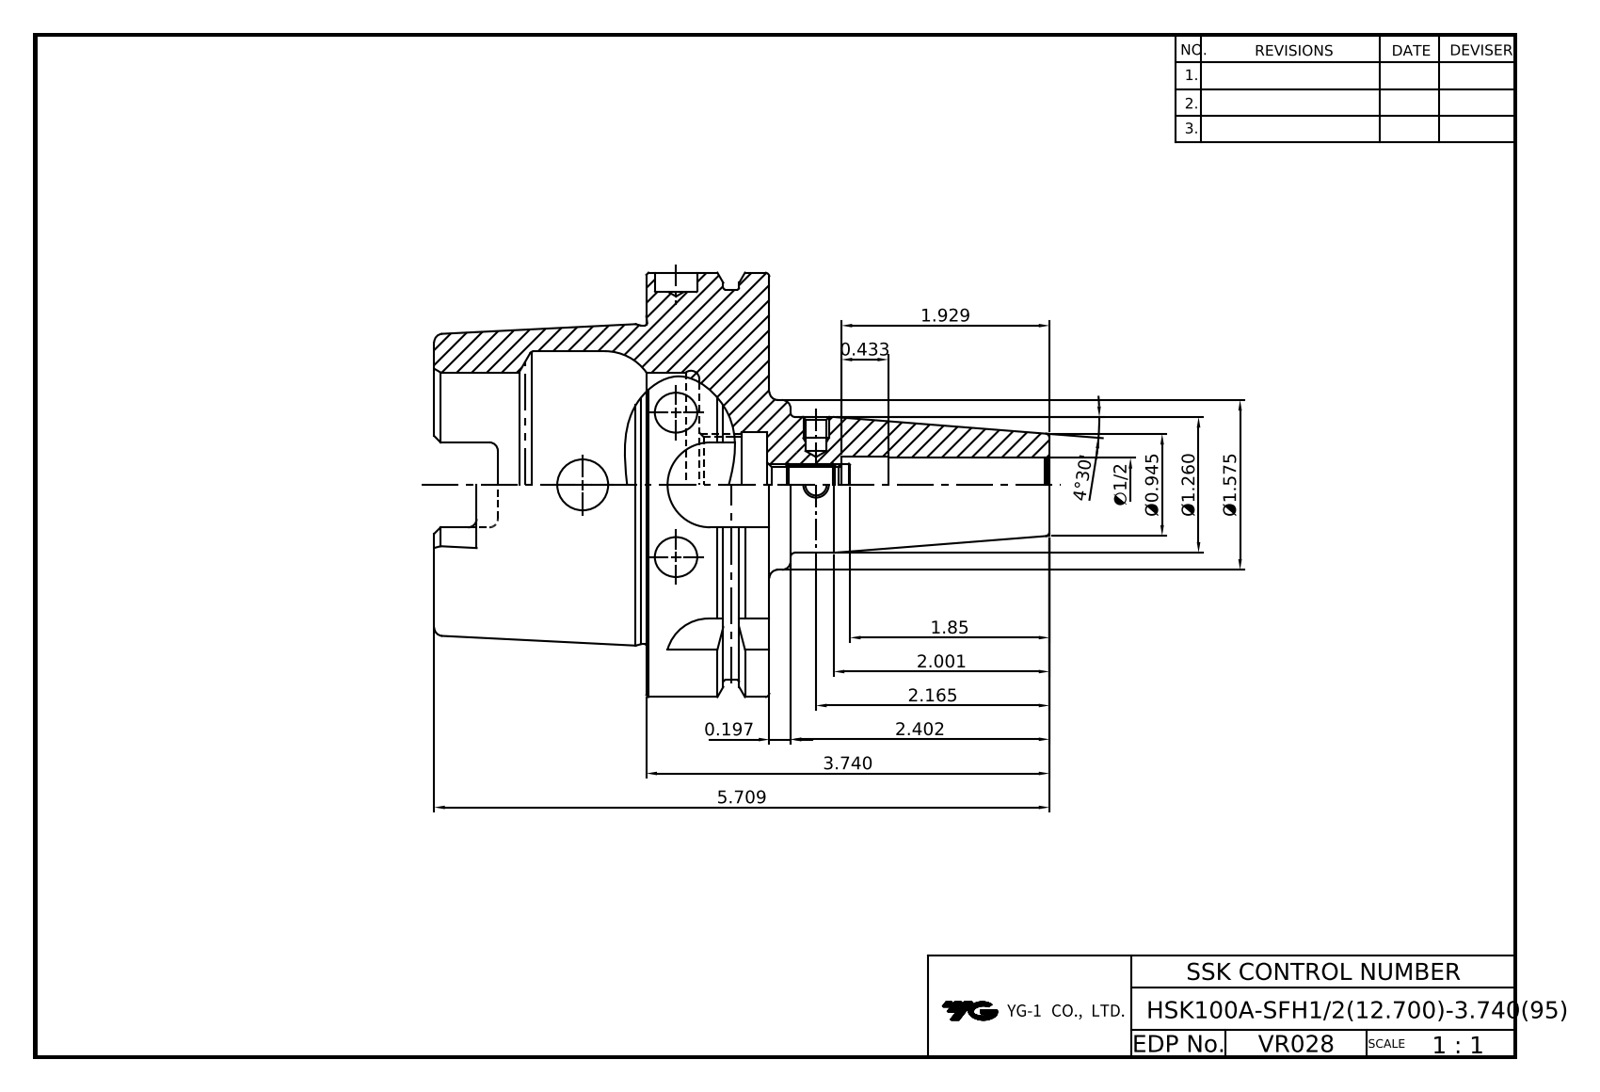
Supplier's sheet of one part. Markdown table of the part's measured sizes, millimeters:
| quantity | value |
| --- | --- |
| part name | HSK100A-SFH12_7-95 |
| STEP written by | CREO PARAMETRIC BY PTC INC, 2018400 (CONFIG_CONTROL_DESIGN) |
| units | millimeters |
| bodies | 1 solid, 216 faces (60 planar, 80 cylindrical, 76 other) |
| overall size | 140 × 100 × 100 |
| volume | 288 913 mm³ |
| surface area | 59 145 mm² |
| round holes (diameter × count) | 7 × 3, 5 × 2, 6 × 2, 8 × 1, 9.53 × 1, 10 × 1, 10.2 × 1, 12 × 1, 22.5 × 1, 24 × 1, 25 × 1, 53 × 1 |
| round bosses / shafts (diameter × count) | 100 × 1, 92 × 1, 75.16 × 1, 40 × 1 |
| partial cylindrical surfaces (radius × count) | 2 × 6, 4.88 × 4, 10 × 4, 16 × 1 |
| main face-to-face distances | 29, 12.5, 16.5, 62.5, 50, 79, 10, 71.88, 68.12, 72.5 |
| hole center spacings | 31, 53 |
